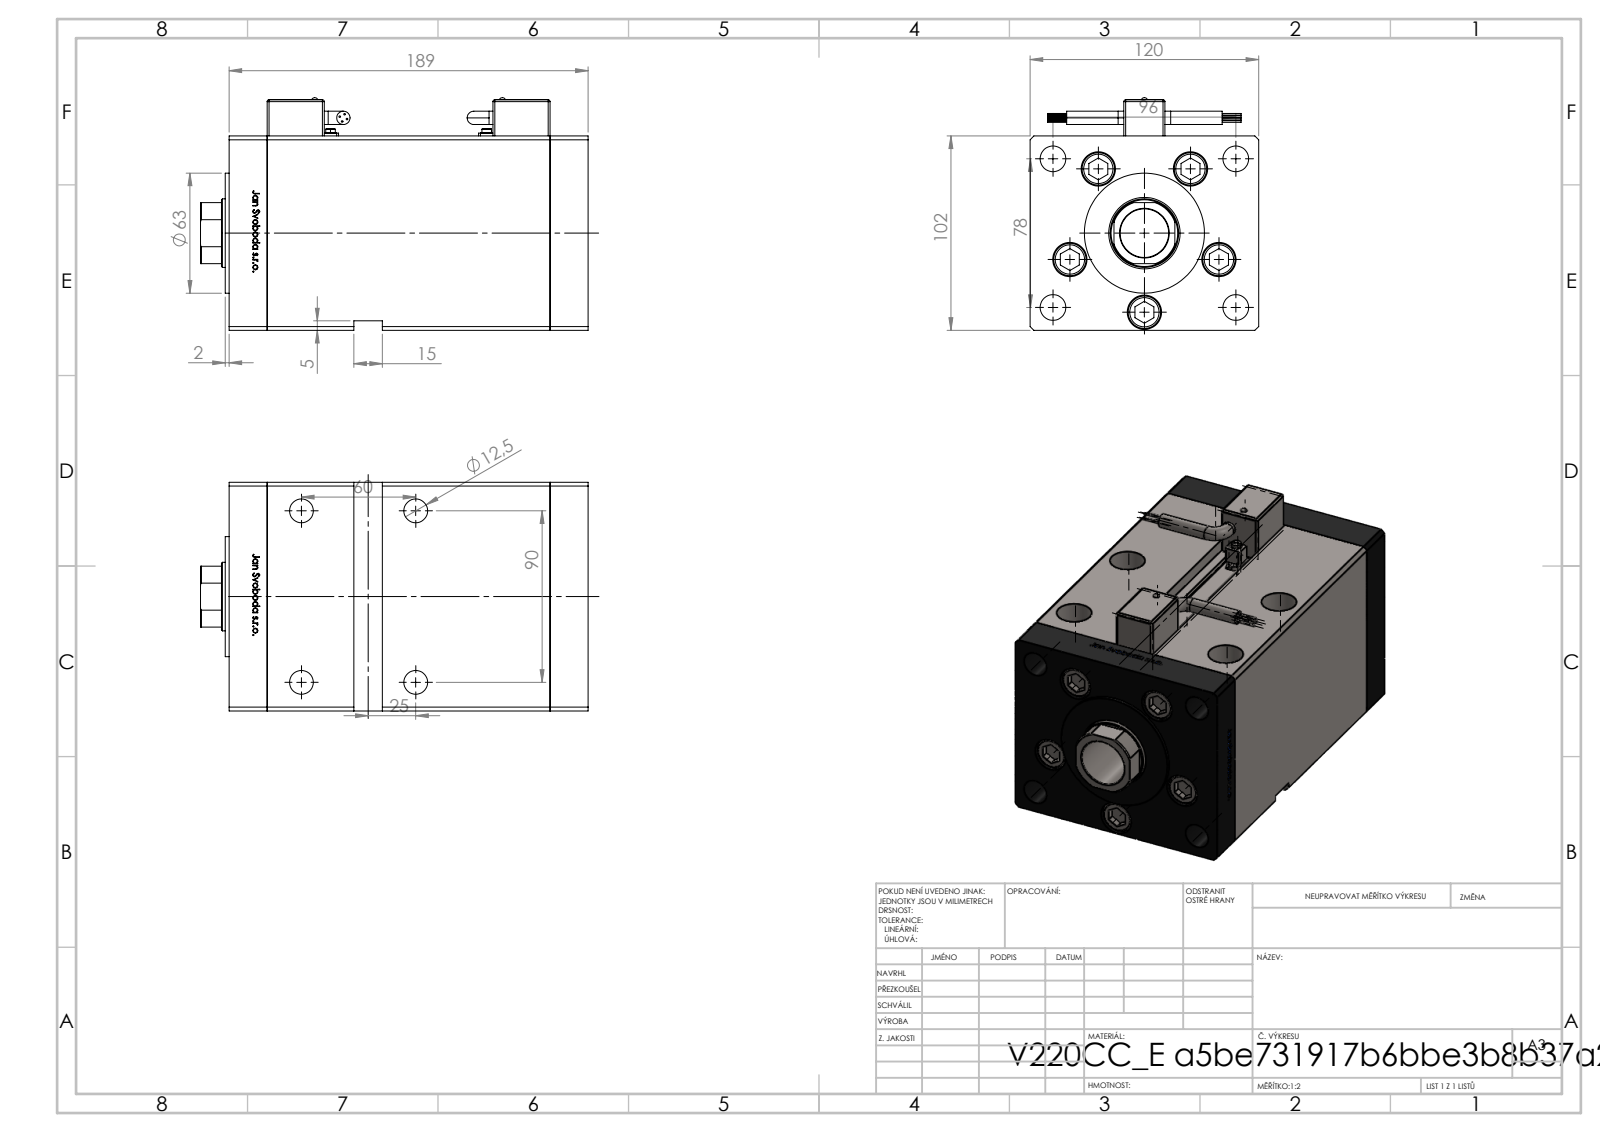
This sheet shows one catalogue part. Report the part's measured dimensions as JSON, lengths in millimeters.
{"part_name": "V220C_VC_E; V220C_FRONT_E; V220C_E MIDDLE; Magnetic_Switch_MSU4 (+2 more)", "step_written_by": "SolidWorks 2019 (CONFIG_CONTROL_DESIGN)", "units": "millimeters", "bodies": {"solids": 16, "faces": 1418, "planar": 553, "cylindrical": 255, "other": 610}, "overall_size": [203.5, 122.1, 120], "volume_mm3": 2010000, "surface_area_mm2": 285085, "round_holes": [[13.5, 9], [18, 5], [12.5, 4], [18.5, 4], [2, 2], [3.6, 2], [5, 2], [7, 2], [13.16, 2], [25.5, 1], [36, 1], [37.5, 1]], "round_bosses_or_shafts": [[0.85, 8], [17, 5], [8, 5], [7, 4], [6, 2], [3.5, 2], [2.5, 2], [63, 1]], "partial_cylinders_radius": [[1, 24], [4, 4], [0.93, 2], [17.5, 1]], "face_to_face_distances": [120, 20, 148.5, 168.5, 102, 34.25, 188.5, 14.25, 134.25, 154.25], "hole_center_spacings": [41.5, 61.85, 8.25, 24.39, 26.69, 45.54, 47.51, 47.92]}
